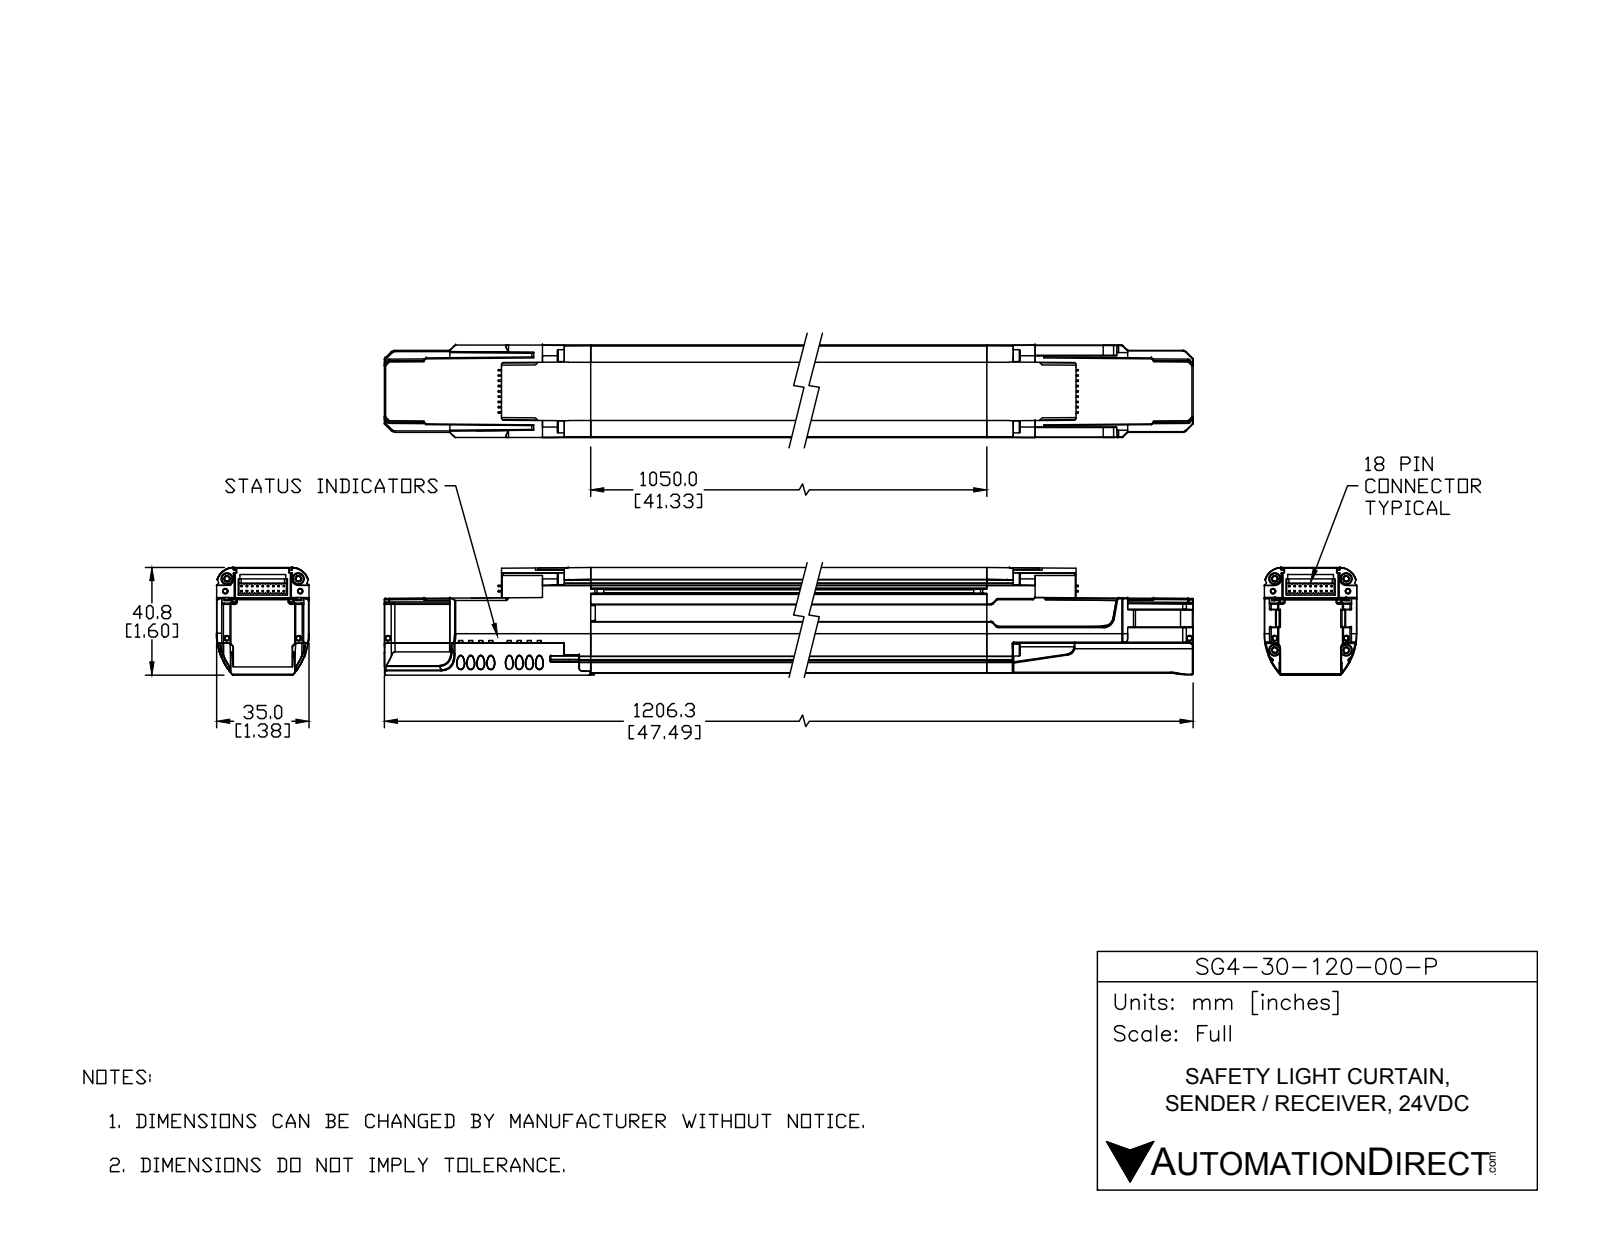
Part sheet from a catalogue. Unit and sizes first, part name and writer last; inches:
Units: inches
Overall size (bounding box): 47.483 × 2.58 × 2.023
Round holes (diameter × count): ⌀0.07 ×6, ⌀0.1 ×4, ⌀0.165 ×4, ⌀0.209 ×4, ⌀0.26 ×4, ⌀0.065 ×1, ⌀0.065 ×1
Round bosses / shafts (diameter × count): ⌀0.394 ×4, ⌀0.197 ×4
Partial cylindrical surfaces — rounded edges, fillets, slot ends (radius × count): R0.106 ×16, R0.118 ×8, R0.1 ×4, R0.11 ×4, R0.08 ×2, R0.12 ×2, R0.123 ×2, R0.125 ×2
Main face-to-face distances: 0.06, 0.084, 0.024, 1.49, 1.466, 1.55, 1.057, 0.481, 0.985, 1.009
Hole centre spacings: 0.569, 39.755, 0.02, 0.204, 0.207, 0.207, 0.227, 0.71
Volume: 90.33 in³ · Surface area: 502.5 in²
Bodies: 16 solids, 534 faces (362 planar, 110 cylindrical, 62 other)
Part name (STEP PRODUCT): SG4-30-120-OO-P
STEP written by: SolidWorks 2017 (AUTOMOTIVE_DESIGN)
